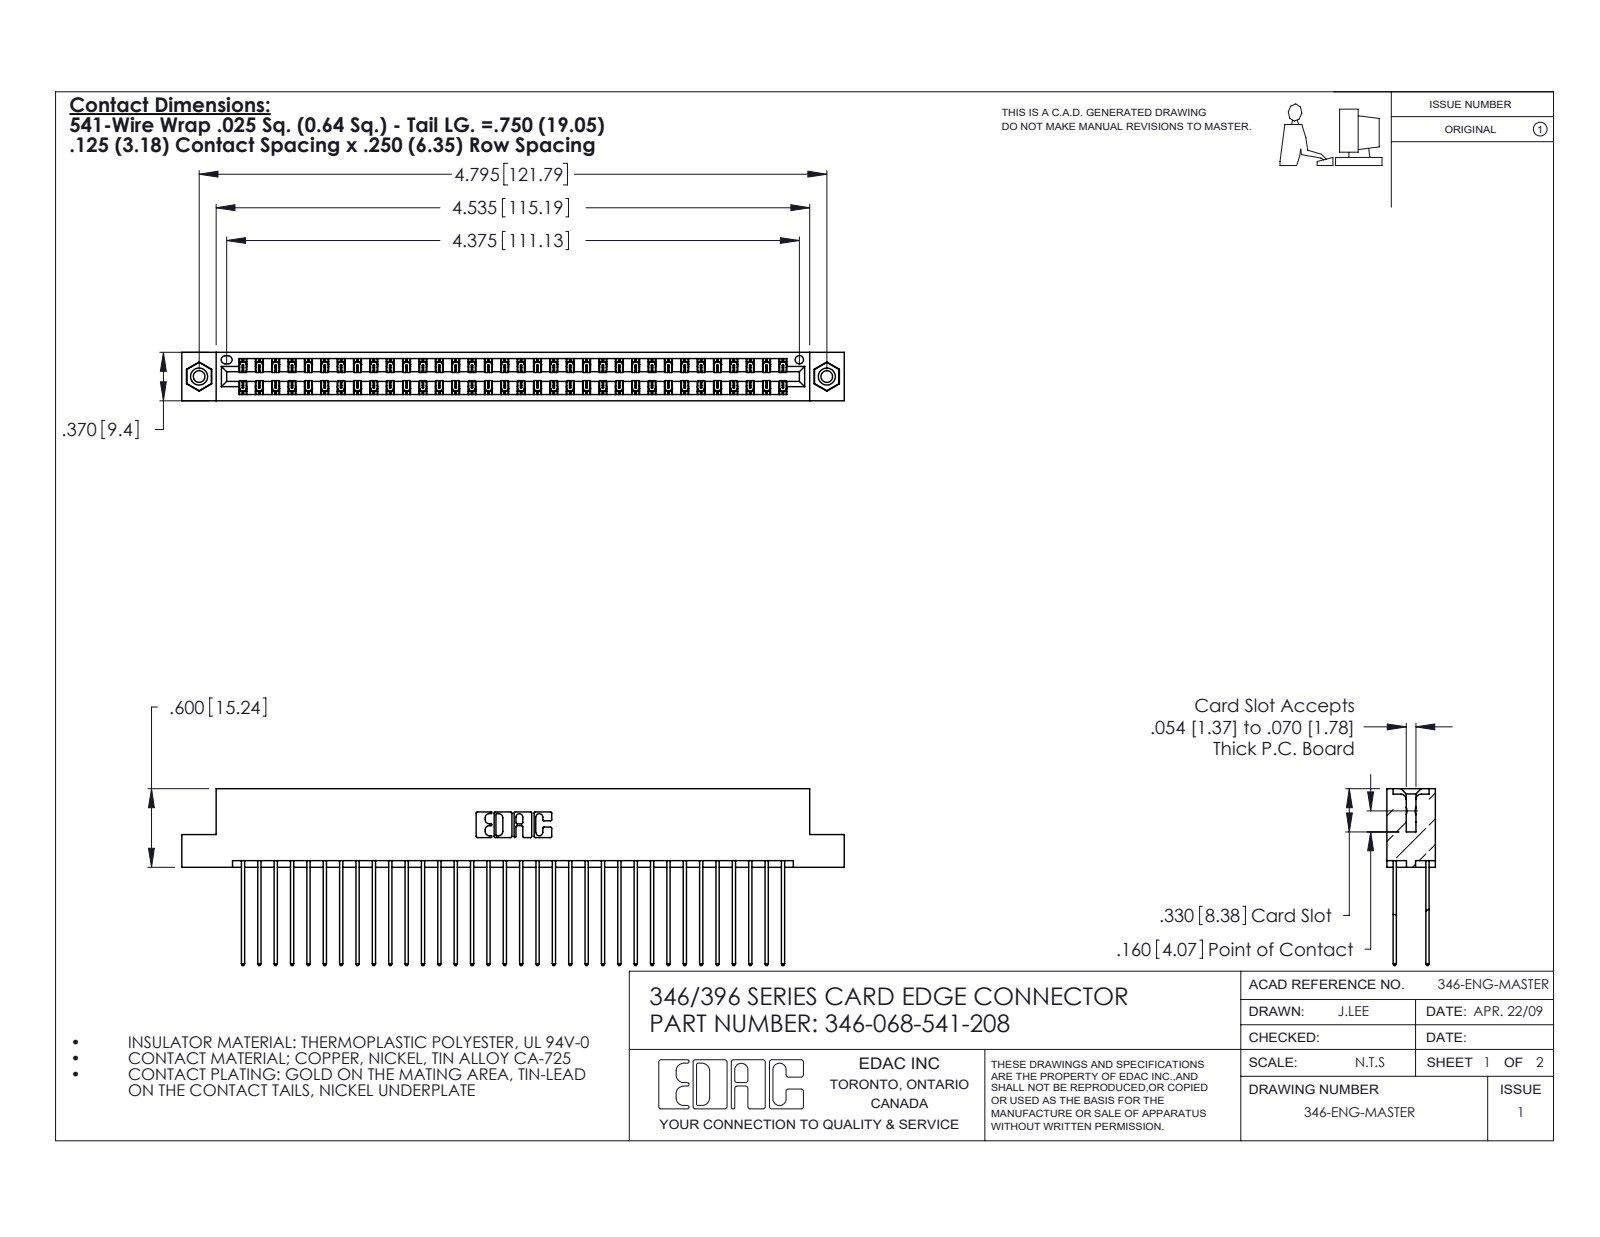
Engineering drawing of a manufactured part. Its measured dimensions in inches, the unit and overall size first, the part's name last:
Units: inches
Overall size (bounding box): 5.06 × 1.35 × 0.37
Round holes (diameter × count): ⌀0.089 ×2, ⌀0.125 ×2, ⌀0.156 ×2, ⌀0.064 ×1
Round bosses / shafts (diameter × count): ⌀0.155 ×2
Partial cylindrical surfaces — rounded edges, fillets, slot ends (radius × count): R0.006 ×102, R0.01 ×68, R0.01 ×22, R0.007 ×6, R0.031 ×6, R0.026 ×3, R0.014 ×2, R0.022 ×2
Main face-to-face distances: 0.048, 0.322, 0.25, 0.072, 0.298, 0.025, 0.37, 0.275, 0.225, 0.148
Hole centre spacings: 0.246, 4.587, 4.795
Volume: 0.784 in³ · Surface area: 30.12 in²
Bodies: 71 solids, 3718 faces (2488 planar, 1214 cylindrical, 16 other)
Part name (STEP PRODUCT): 346-068-541-208; 346 Part_Flush Mounting Lugs - 0.156 Dia-TI; 345-250-001_345-250-003-102; 345-292-001_345-293-141
STEP written by: SolidWorks 2020 (CONFIG_CONTROL_DESIGN)
